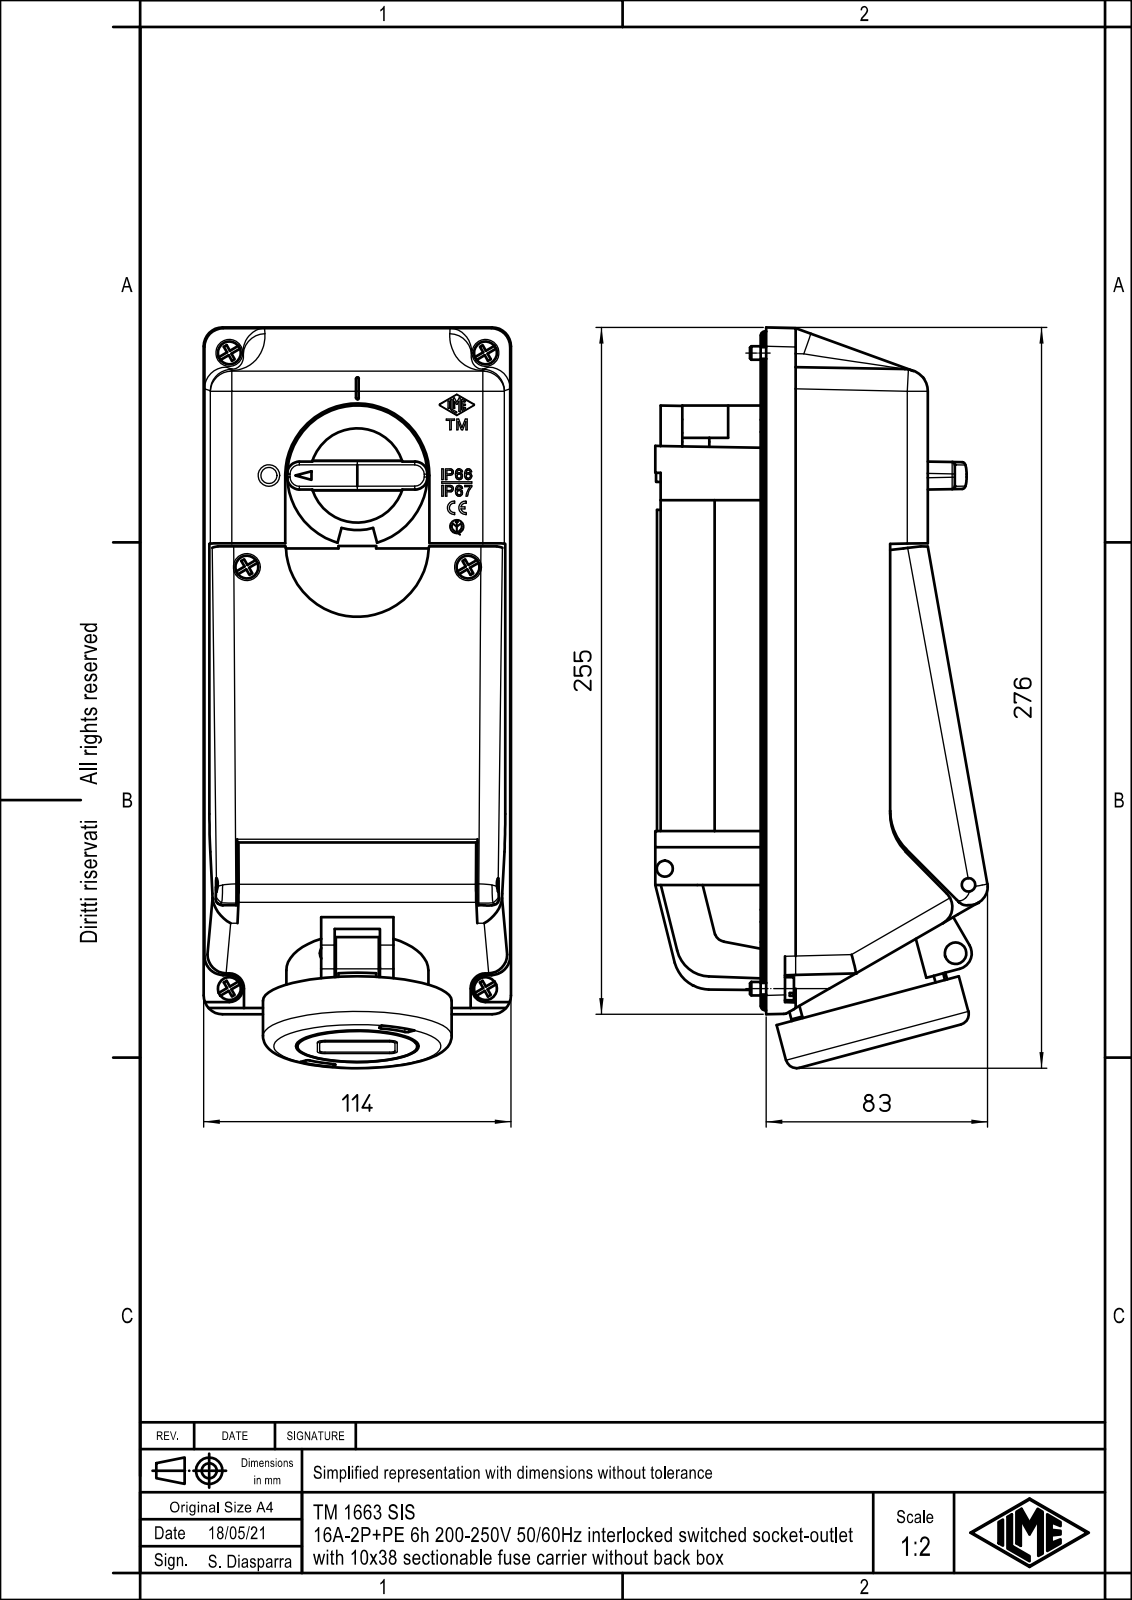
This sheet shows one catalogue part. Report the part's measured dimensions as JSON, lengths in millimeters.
{"part_name": "TM_1663SIS", "step_written_by": "Creo Elements/Direct Modeling 20.1B 02-Apr-2019 (C) Parametric Technology GmbH (AUTOMOTIVE_DESIGN)", "units": "millimeters", "bodies": {"solids": 1, "faces": 1274, "planar": 883, "cylindrical": 295, "other": 96}, "overall_size": [275.02, 123.3, 114], "volume_mm3": 2376000, "surface_area_mm2": 168601, "round_holes": [[10, 3], [4.75, 1], [5, 1], [6, 1], [8, 1], [35, 1], [43.4, 1], [45.5, 1]], "round_bosses_or_shafts": [[8.5, 6], [5, 4], [4.3, 4], [8, 2], [70, 1], [52.7, 1], [52, 1], [44.5, 1]], "partial_cylinders_radius": [[1.5, 18], [5, 18], [1, 17], [2, 15], [6, 14], [7, 12], [0.25, 11], [3, 8]], "face_to_face_distances": [35.3, 3, 92.4, 35.1, 60, 95.1, 59.8, 5.3, 4, 89.4], "hole_center_spacings": [65.78, 25.79, 32.85, 41.5, 47.8, 65.37, 72.29, 92.34]}
